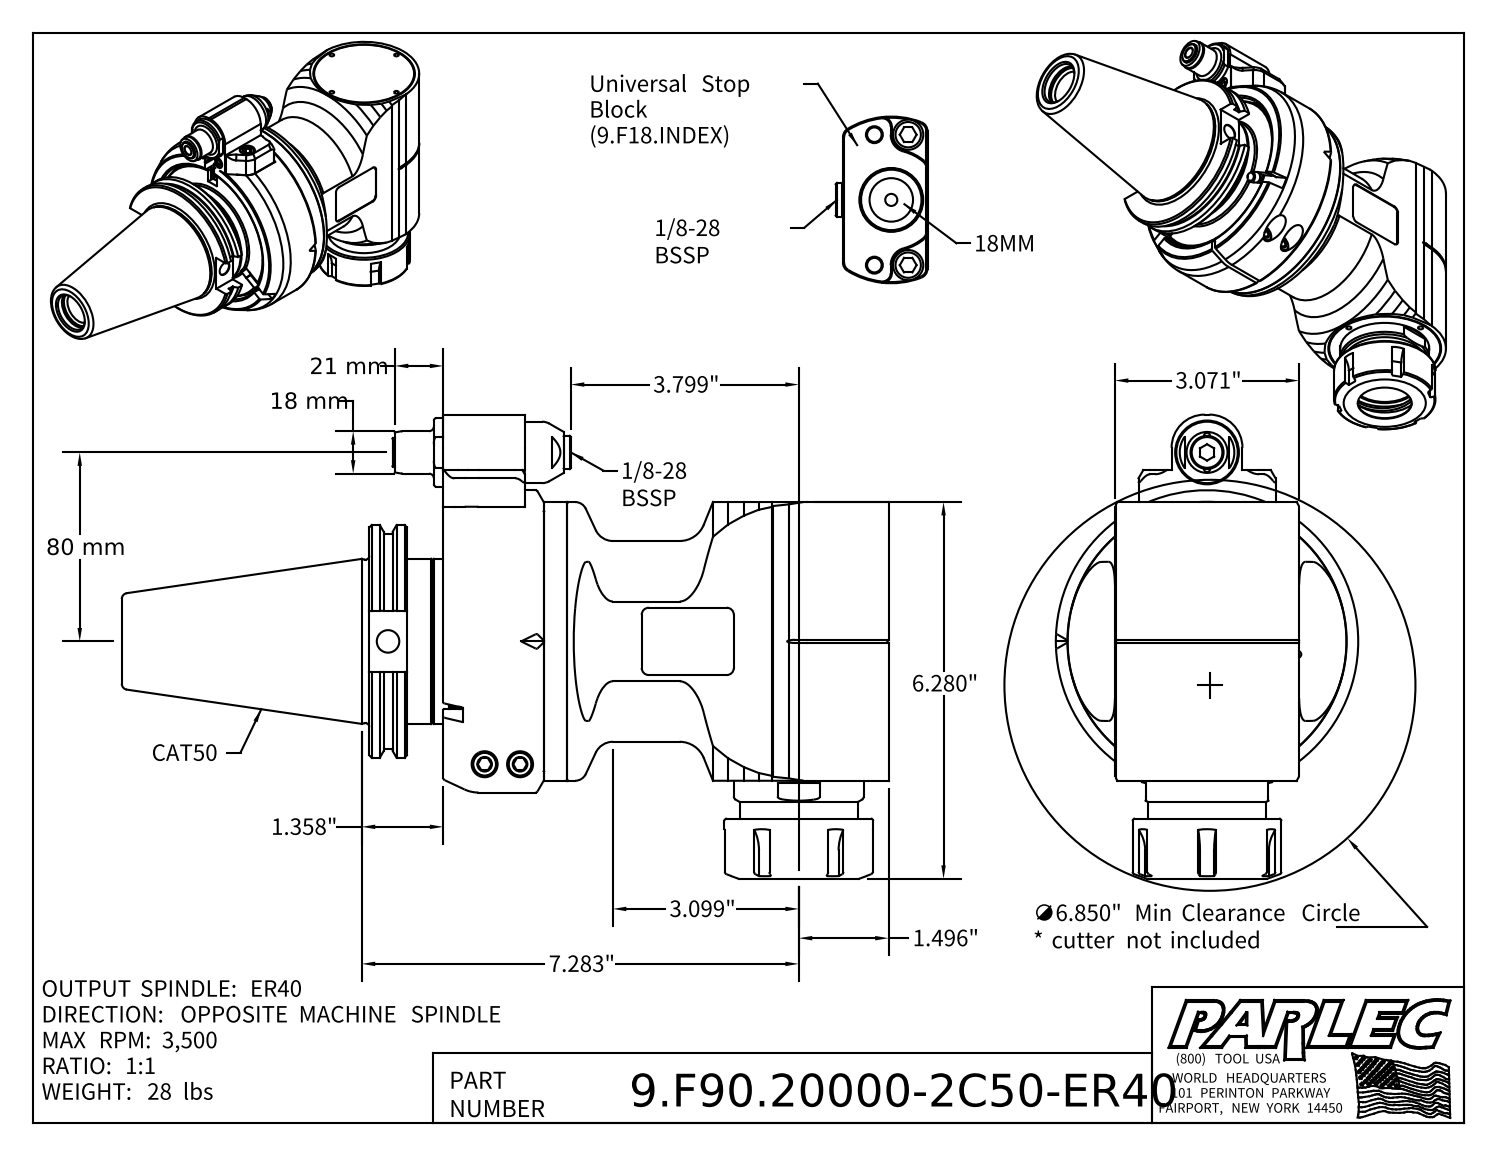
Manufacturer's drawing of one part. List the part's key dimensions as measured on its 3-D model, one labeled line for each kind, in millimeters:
Part name (STEP PRODUCT): 9.F90.20000-2C50-ER40
STEP written by: Autodesk Inventor 2022 (AUTOMOTIVE_DESIGN)
Units: millimetres
Bodies: 1 solid, 680 faces (302 planar, 180 cylindrical, 198 other)
Overall size (bounding box): 324.6 × 196.5 × 128
Volume: 2 097 000 mm³ · Surface area: 197 019 mm²
Round holes (diameter × count): ⌀3.2 ×8, ⌀6.5 ×3, ⌀12.5 ×3, ⌀2.6 ×2, ⌀3.3 ×2, ⌀4.2 ×2, ⌀5 ×2, ⌀8 ×2, ⌀10.4 ×2, ⌀11 ×2, ⌀13 ×2, ⌀2.5 ×1
Round bosses / shafts (diameter × count): ⌀10 ×4, ⌀12 ×3, ⌀55 ×2, ⌀18 ×2, ⌀6 ×2, ⌀2.5 ×2, ⌀128 ×1, ⌀118.2 ×1
Partial cylindrical surfaces — rounded edges, fillets, slot ends (radius × count): R1 ×14, R3 ×10, R2 ×8, R15 ×6, R4 ×4, R0.4 ×2, R0.5 ×2, R3.5 ×2
Main face-to-face distances: 6, 78, 0.5, 8.5, 17.95, 23.95, 1, 7, 5, 2.5
Hole centre spacings: 31.5, 34, 44.55, 48.08, 7, 12.81, 18.79, 25.3
